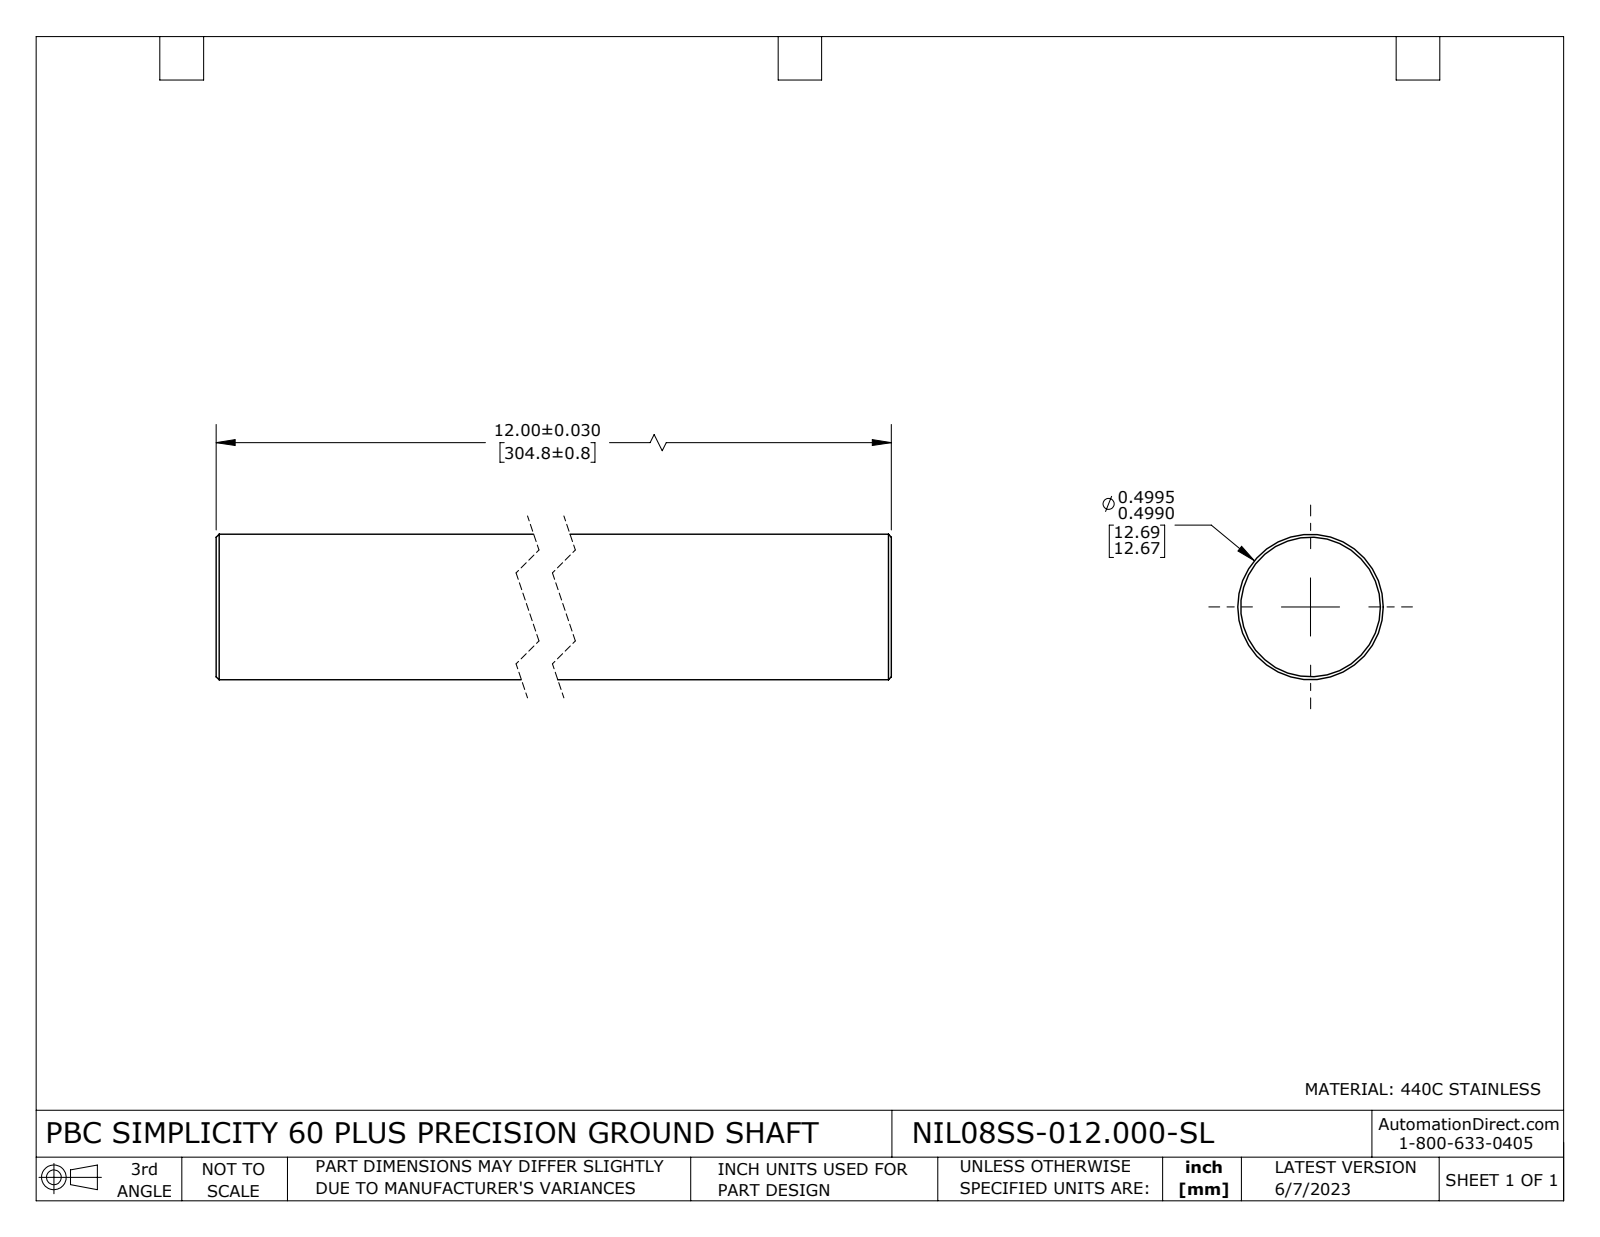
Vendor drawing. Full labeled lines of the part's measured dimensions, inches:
Part name (STEP PRODUCT): NIL08SS-012.000-SL
STEP written by: SolidWorks 2021 (CONFIG_CONTROL_DESIGN)
Units: inches
Bodies: 1 solid, 8 faces (2 planar, 2 cylindrical, 4 other)
Overall size (bounding box): 12 × 0.5 × 0.5
Volume: 2.356 in³ · Surface area: 19.22 in²
Round bosses / shafts (diameter × count): ⌀0.5 ×1
Main face-to-face distances: 12
